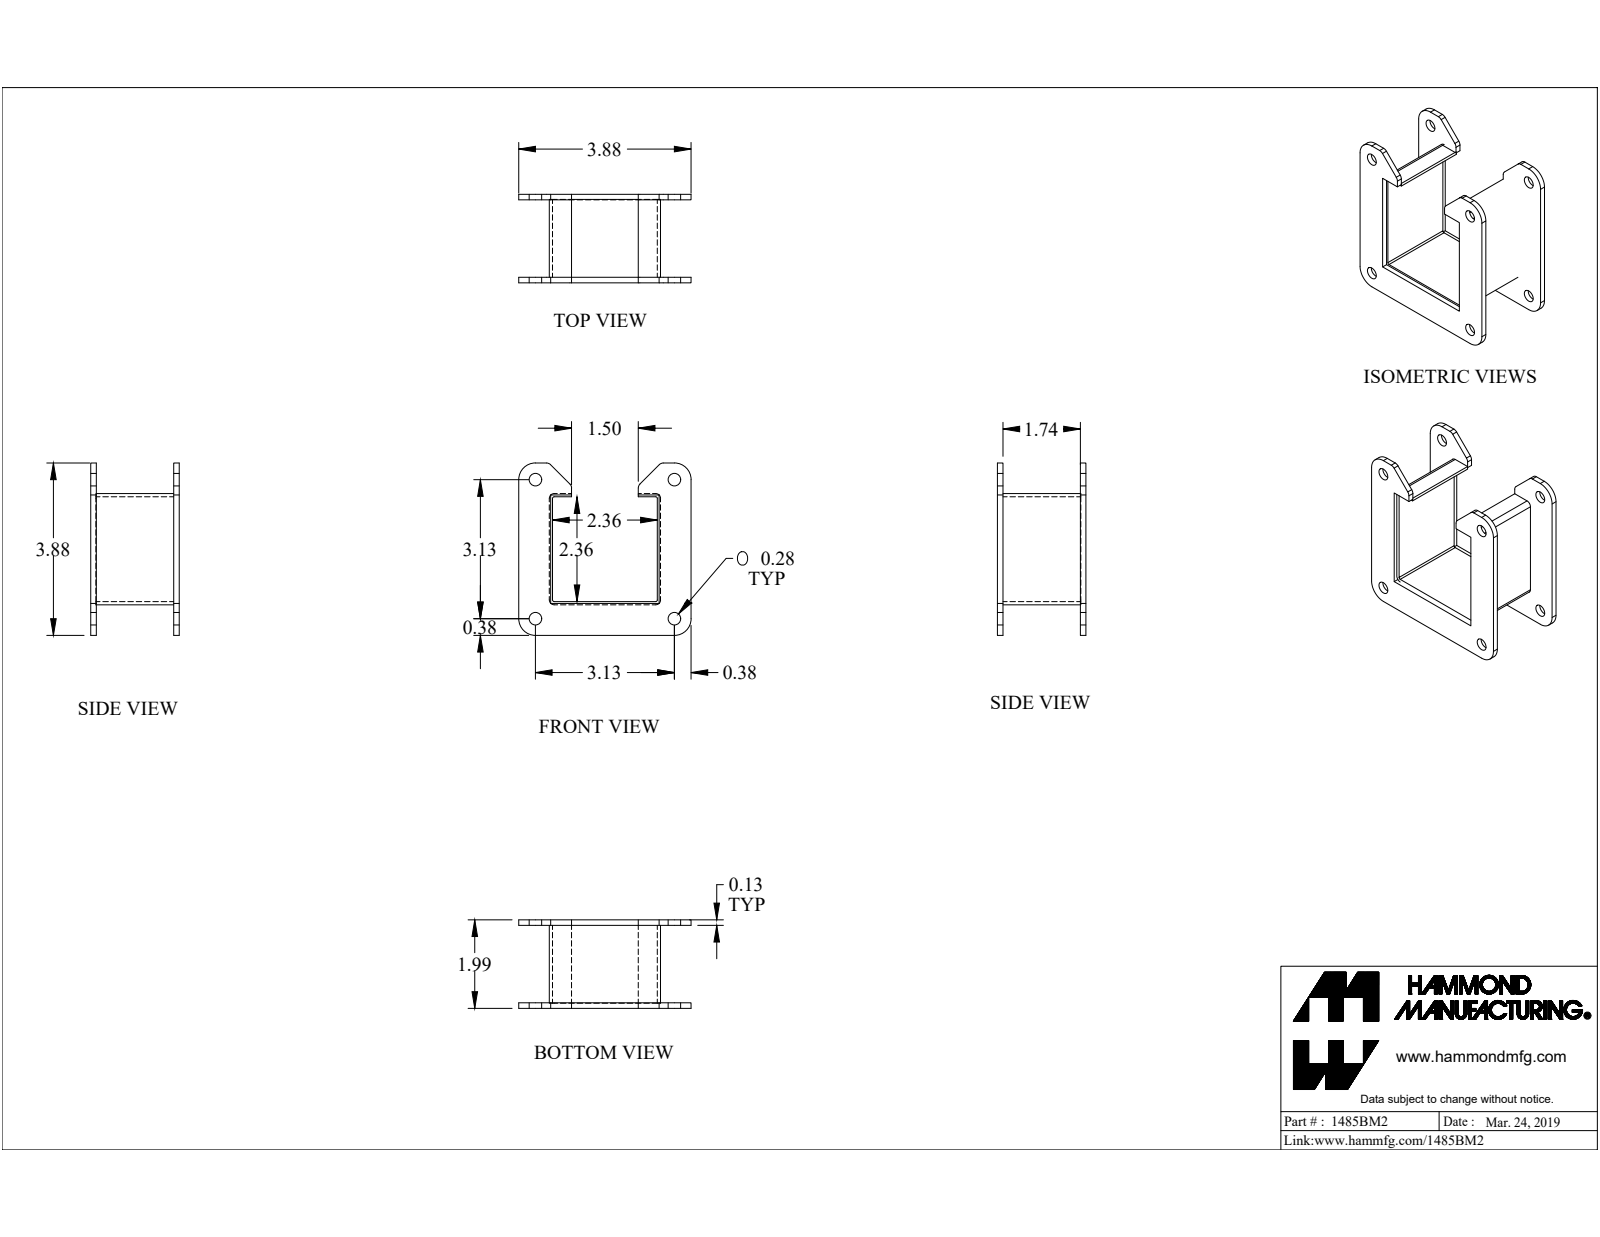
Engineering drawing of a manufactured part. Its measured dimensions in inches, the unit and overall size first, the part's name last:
Units: inches
Overall size (bounding box): 3.875 × 3.875 × 1.99
Round holes (diameter × count): ⌀0.281 ×4
Partial cylindrical surfaces — rounded edges, fillets, slot ends (radius × count): R0.036 ×4, R0.108 ×4, R0.125 ×4, R0.375 ×4
Main face-to-face distances: 1.865, 0.125, 0.072, 2.428, 1.99, 1.74, 2.5, 2.356, 0.687, 0.759
Hole centre spacings: 3.125, 4.42
Volume: 2.859 in³ · Surface area: 65.65 in²
Bodies: 3 solids, 78 faces (46 planar, 32 cylindrical, 0 other)
Part name (STEP PRODUCT): 1485BM2
STEP written by: SolidWorks 2019 (CONFIG_CONTROL_DESIGN)
